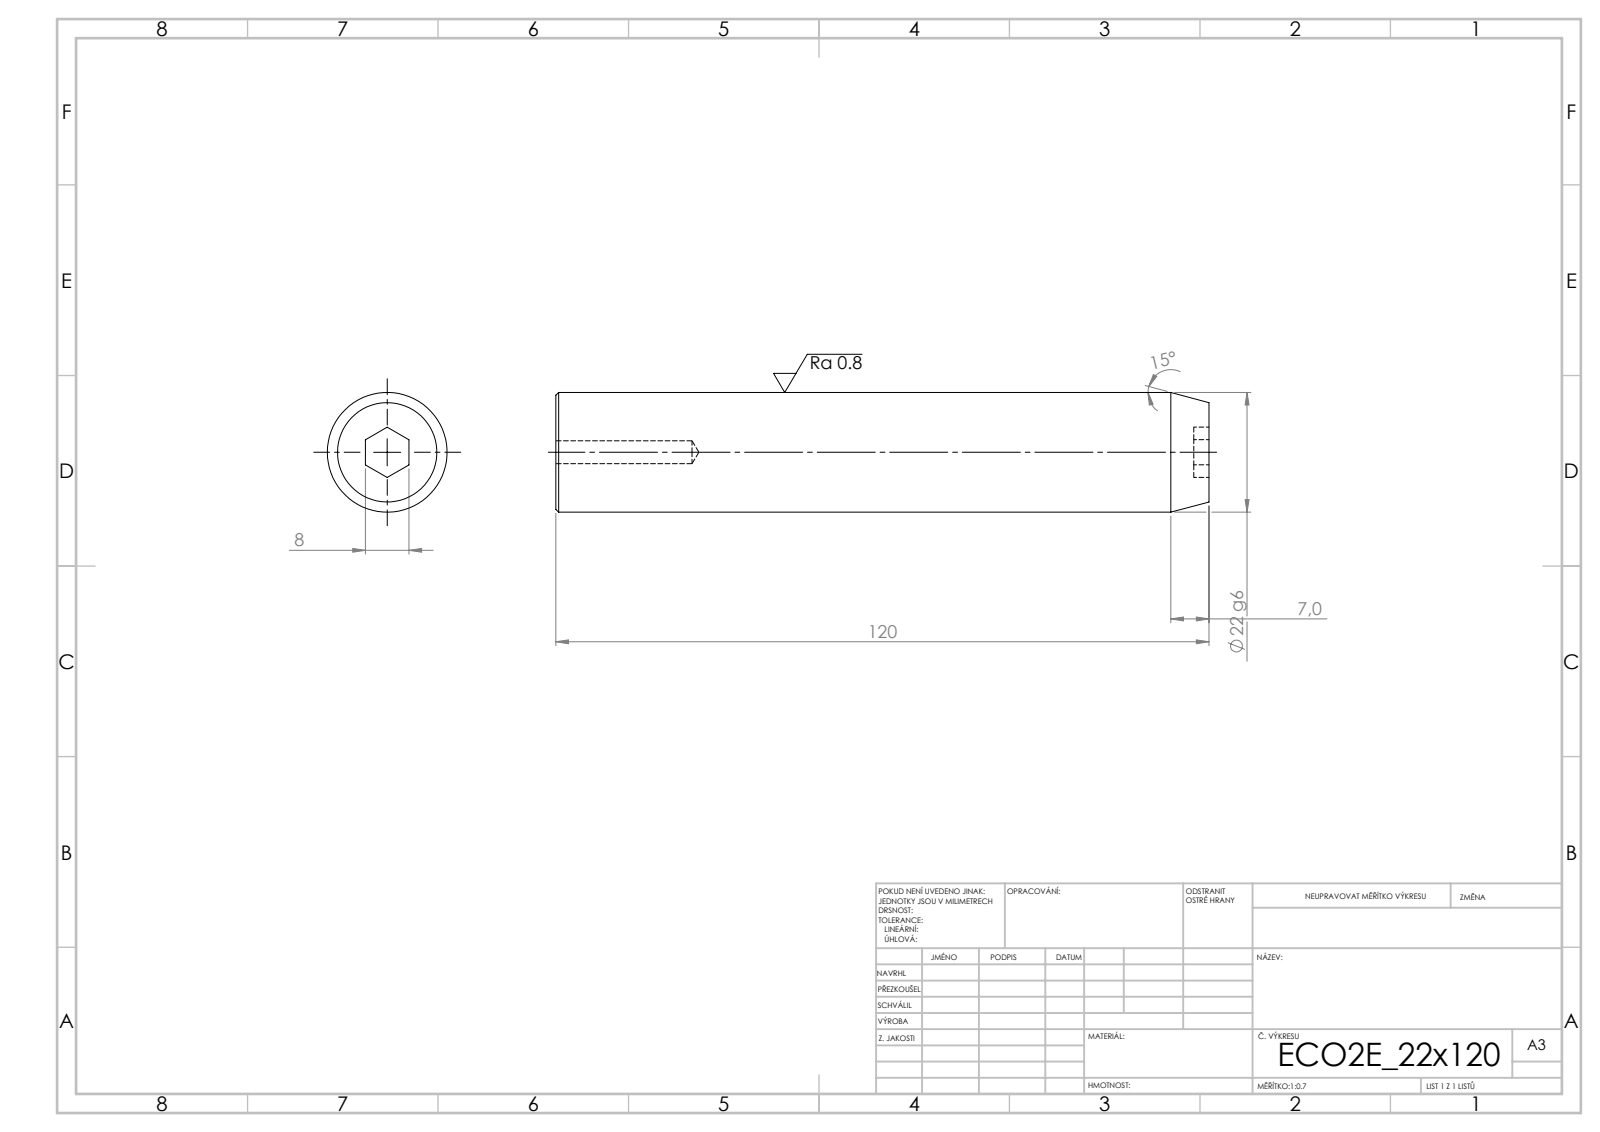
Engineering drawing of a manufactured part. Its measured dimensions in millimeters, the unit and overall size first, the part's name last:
Units: millimetres
Overall size (bounding box): 120 × 22 × 22
Round holes (diameter × count): ⌀4.2 ×1
Round bosses / shafts (diameter × count): ⌀22 ×1
Main face-to-face distances: 120, 2.8, 117.2, 8
Volume: 44 672 mm³ · Surface area: 9 299 mm²
Bodies: 1 solid, 19 faces (9 planar, 4 cylindrical, 6 other)
STEP written by: SolidWorks 2019 (CONFIG_CONTROL_DESIGN)
